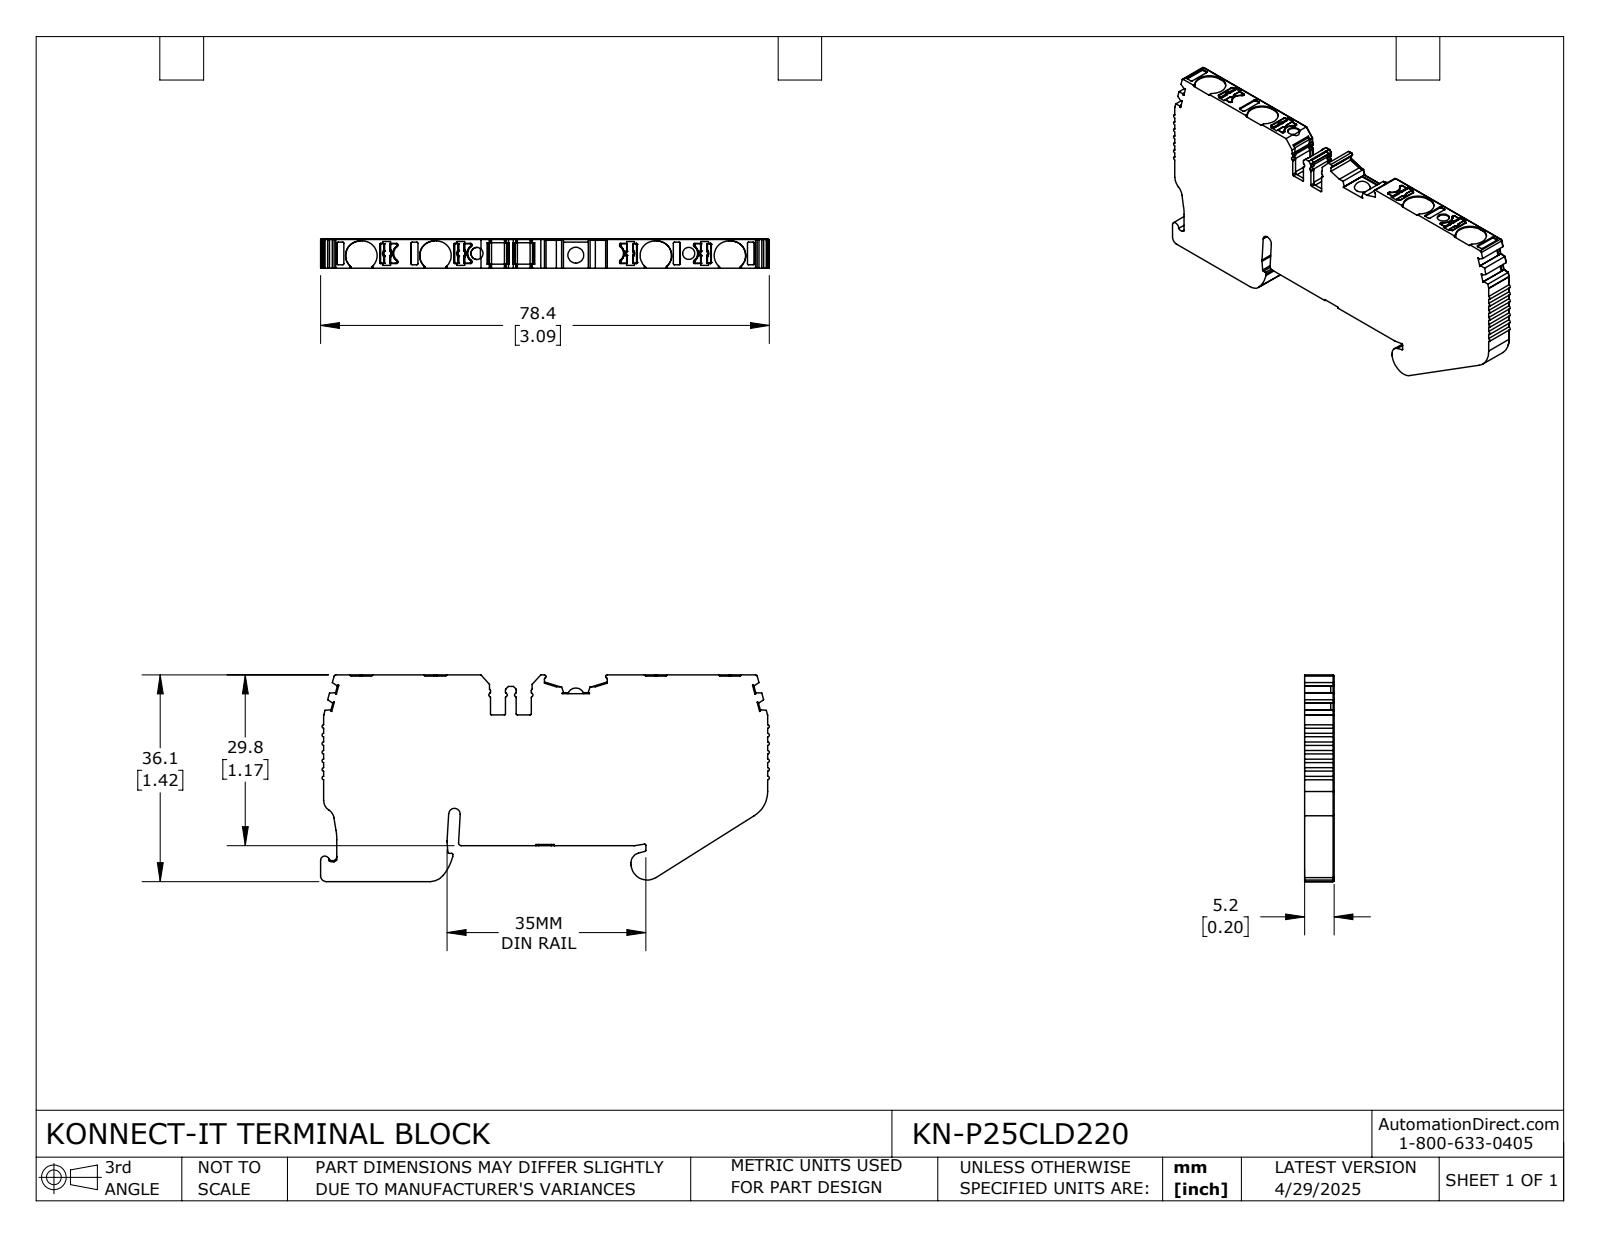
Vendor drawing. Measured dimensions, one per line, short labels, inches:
name: KN-P25CLD220
written by: SolidWorks 2024 (CONFIG_CONTROL_DESIGN)
unit: in
bodies: 1 solid, 740 faces (381 planar, 291 cylindrical, 68 other)
size: 3.085 × 1.42 × 0.203
volume: 0.731 in³; area: 9.643 in²
holes: 2× ⌀0.083
rounds: 78× R0.008, 39× R0.012, 21× R0.004, 18× R0.02, 16× R0.006, 9× R0.016, 8× R0.1, 4× R0.059
face distances: 0.203, 1.166, 1.174, 0.246, 1.412, 1.42, 3.052, 0.047, 0.197, 0.177
hole spacings: 1.456
